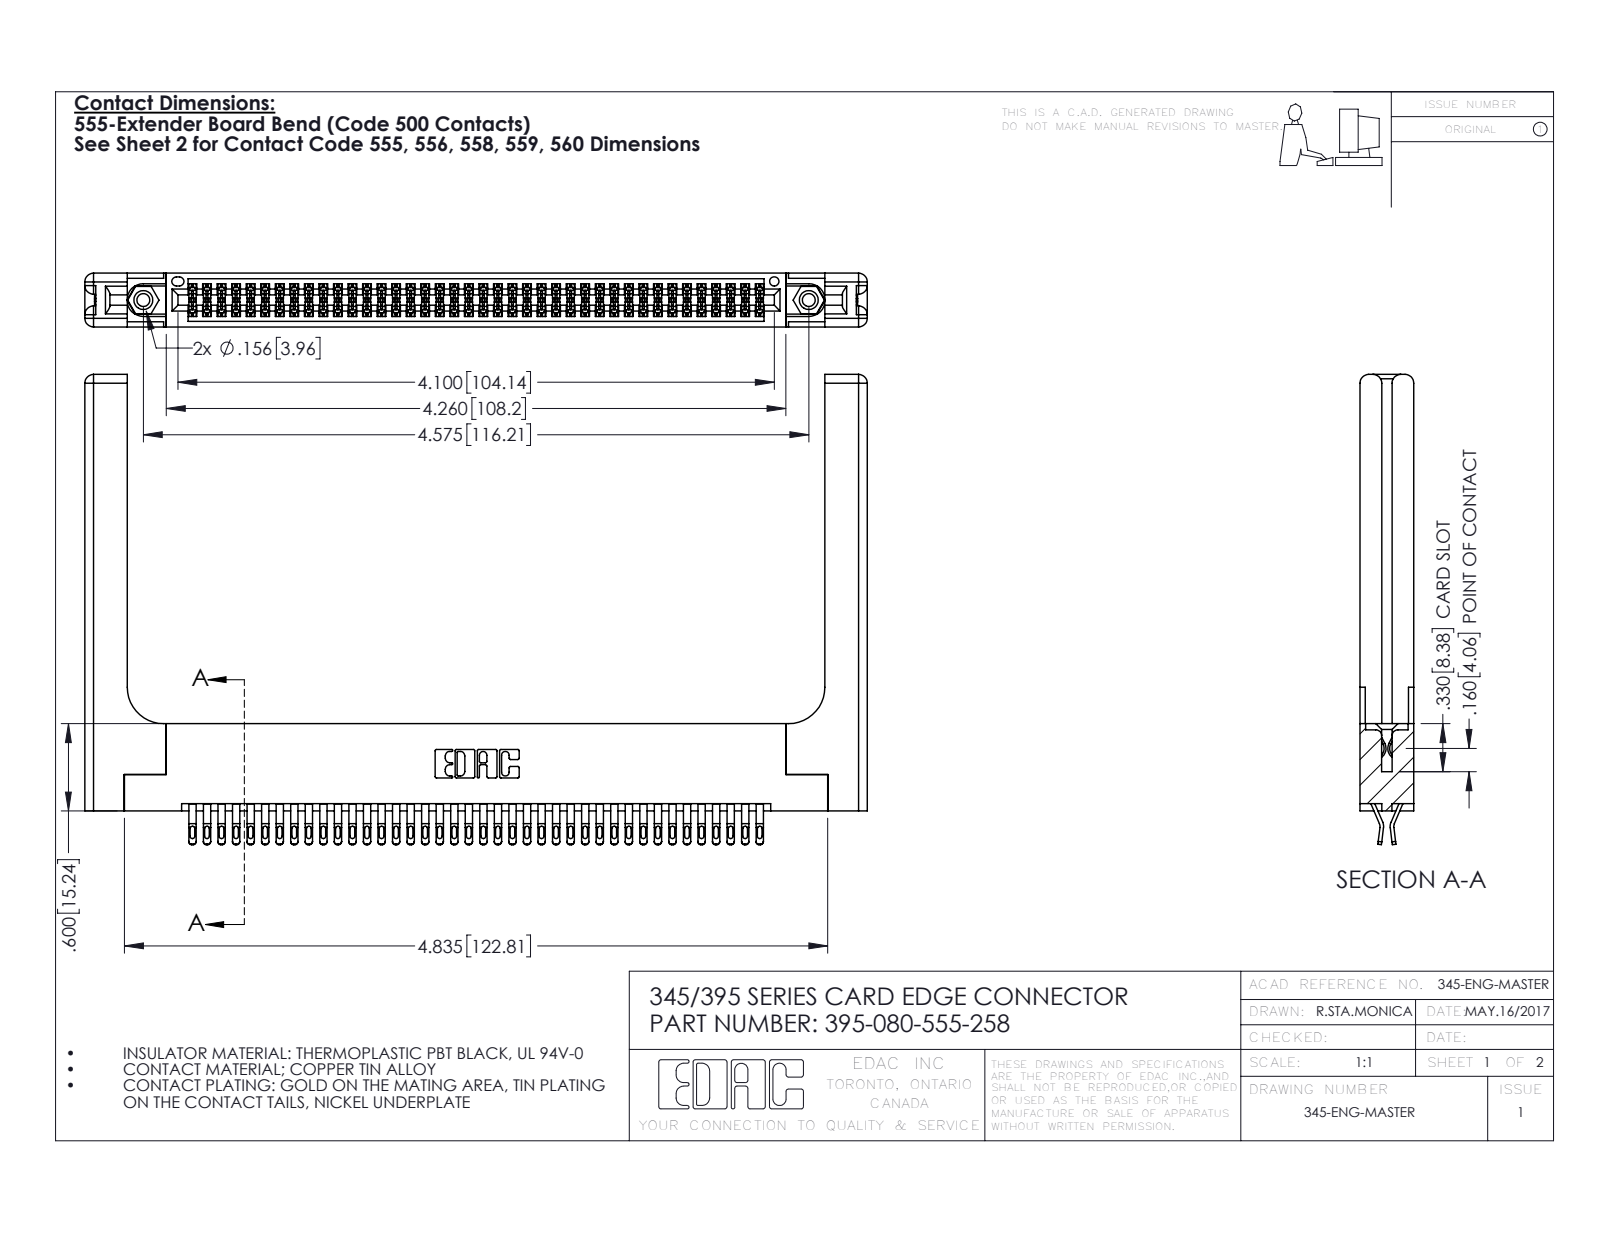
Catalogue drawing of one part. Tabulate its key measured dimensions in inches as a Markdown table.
| quantity | value |
| --- | --- |
| part name | 345-220-058_345-220-058; 345-250-001_345-250-001-102; 345 Part_Flush Mounting Lugs - 0.156 Dia-TH; 395-080-555-258 (+1 more) |
| STEP written by | SolidWorks 2016 (CONFIG_CONTROL_DESIGN) |
| units | inches |
| bodies | 85 solids, 4862 faces (2708 planar, 2094 cylindrical, 60 other) |
| overall size | 5.379 × 3.232 × 0.37 |
| volume | 1.34 in³ |
| surface area | 39.93 in² |
| round holes (diameter × count) | 0.089 × 2, 0.125 × 2, 0.156 × 2, 0.064 × 1 |
| round bosses / shafts (diameter × count) | 0.155 × 2 |
| partial cylindrical surfaces (radius × count) | 0.016 × 200, 0.02 × 160, 0.006 × 120, 0.01 × 22, 0.06 × 16, 0.007 × 6, 0.031 × 6, 0.026 × 3 |
| main face-to-face distances | 0.072, 0.37, 0.298, 0.025, 0.2, 0.098, 0.272, 0.225, 0.148, 0.15 |
| hole center spacings | 0.27, 4.339, 4.575 |
